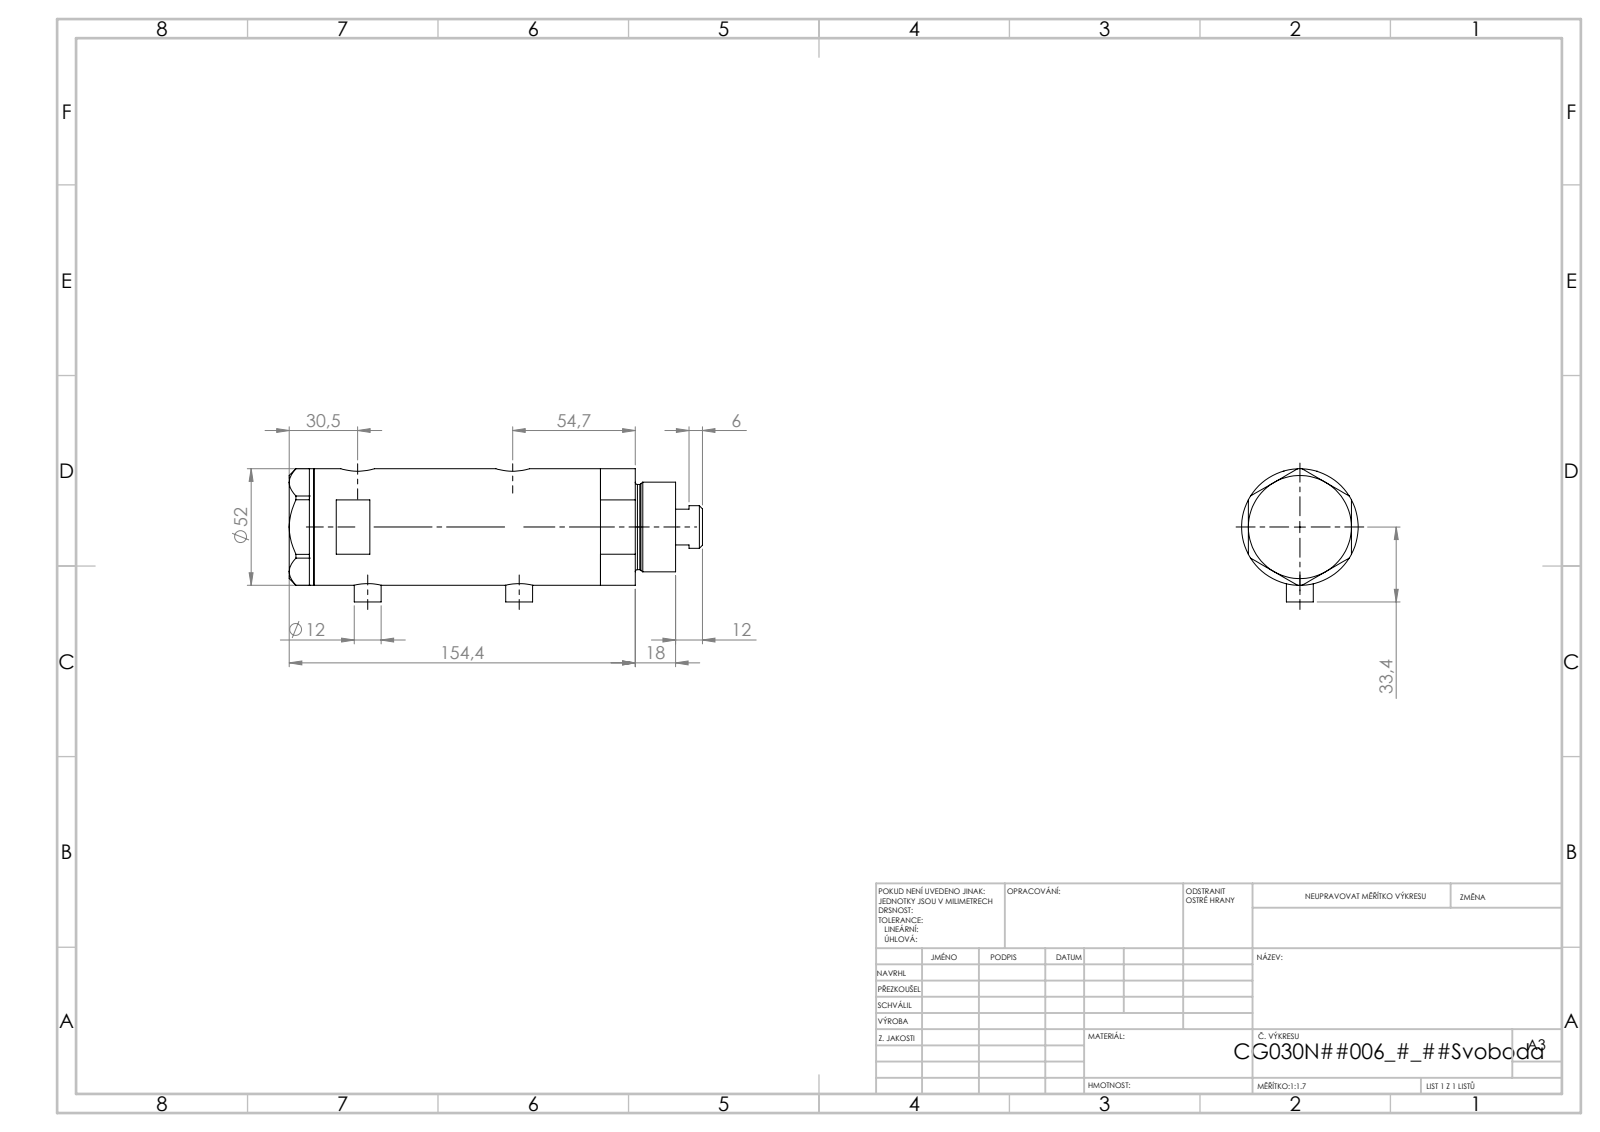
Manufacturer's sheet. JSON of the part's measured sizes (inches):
{"part_name": "V270CG_MIDDLE; V270CG_FRONT; V270CG_BACK; V270CG_VC", "step_written_by": "SolidWorks 2019 (CONFIG_CONTROL_DESIGN)", "units": "inches", "bodies": {"solids": 4, "faces": 140, "planar": 67, "cylindrical": 53, "other": 20}, "overall_size": [7.26, 2.339, 2.047], "volume_in3": 20.97, "surface_area_in2": 121.3, "round_holes": [[0.197, 2], [0.383, 2], [0.492, 2], [0.591, 2], [0.256, 1], [0.787, 1], [0.846, 1], [1.181, 1], [1.299, 1], [1.732, 1]], "round_bosses_or_shafts": [[0.472, 2], [2.047, 1], [1.575, 1], [1.496, 1], [0.748, 1]], "face_to_face_distances": [3.602, 0.937, 2.665, 0.433, 1.37, 4.035, 1.811, 5.469, 5.035, 4.098], "hole_center_spacings": [0.114, 0.177, 2.547, 2.661, 2.724, 2.839]}
